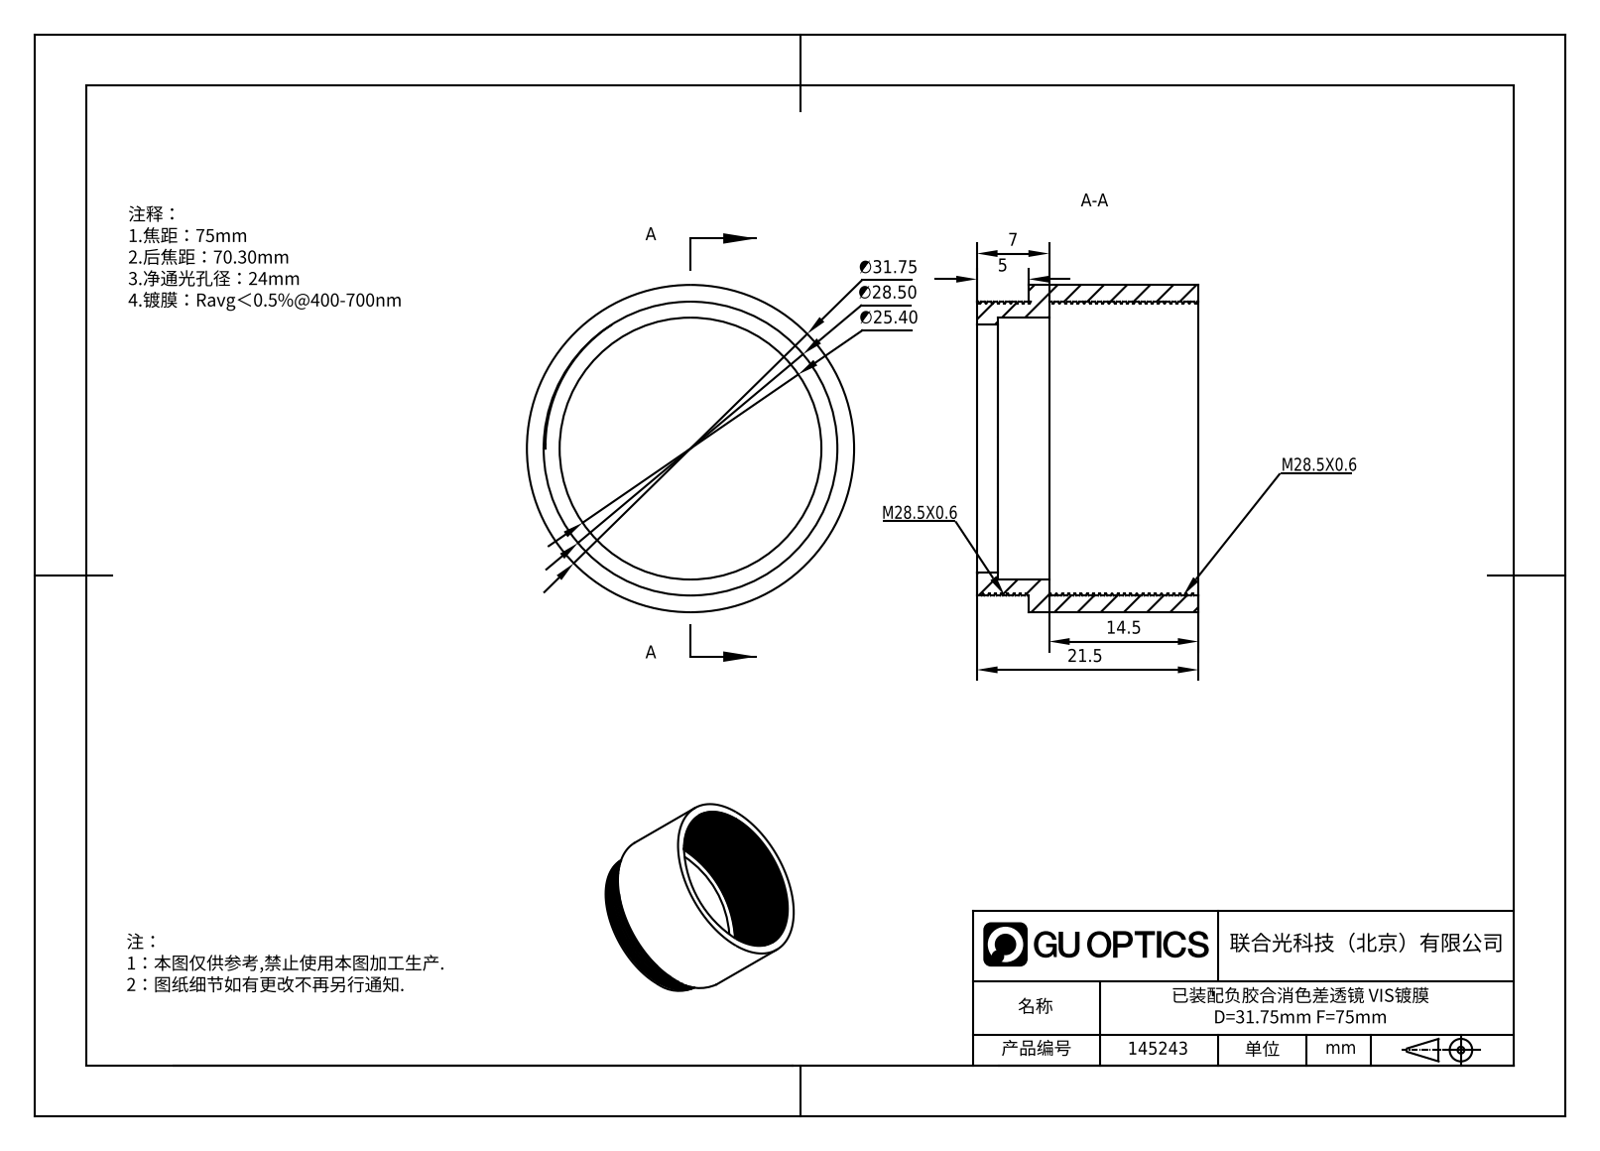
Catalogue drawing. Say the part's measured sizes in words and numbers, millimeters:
The part is named "APD-ML25-075-VIS". Its 3-D file was written by "SolidWorks 2023 (CONFIG_CONTROL_DESIGN)". It is 1 solid with 91 faces: 9 planar, 75 cylindrical and 7 other. Overall it measures 31.75 by 31.75 by 21.5 millimeters. Its volume is 3 609 cubic millimeters and its surface area 6 096 square millimeters. Round holes: 1 of diameter 24, 1 of diameter 25.4, 1 of diameter 28.5. Round bosses or shafts: 1 of diameter 31.75. The main face-to-face distances are 2, 5, 2.01, 21.5, 19.5, 19.49, 3, 2.99, 16.5, 7.
